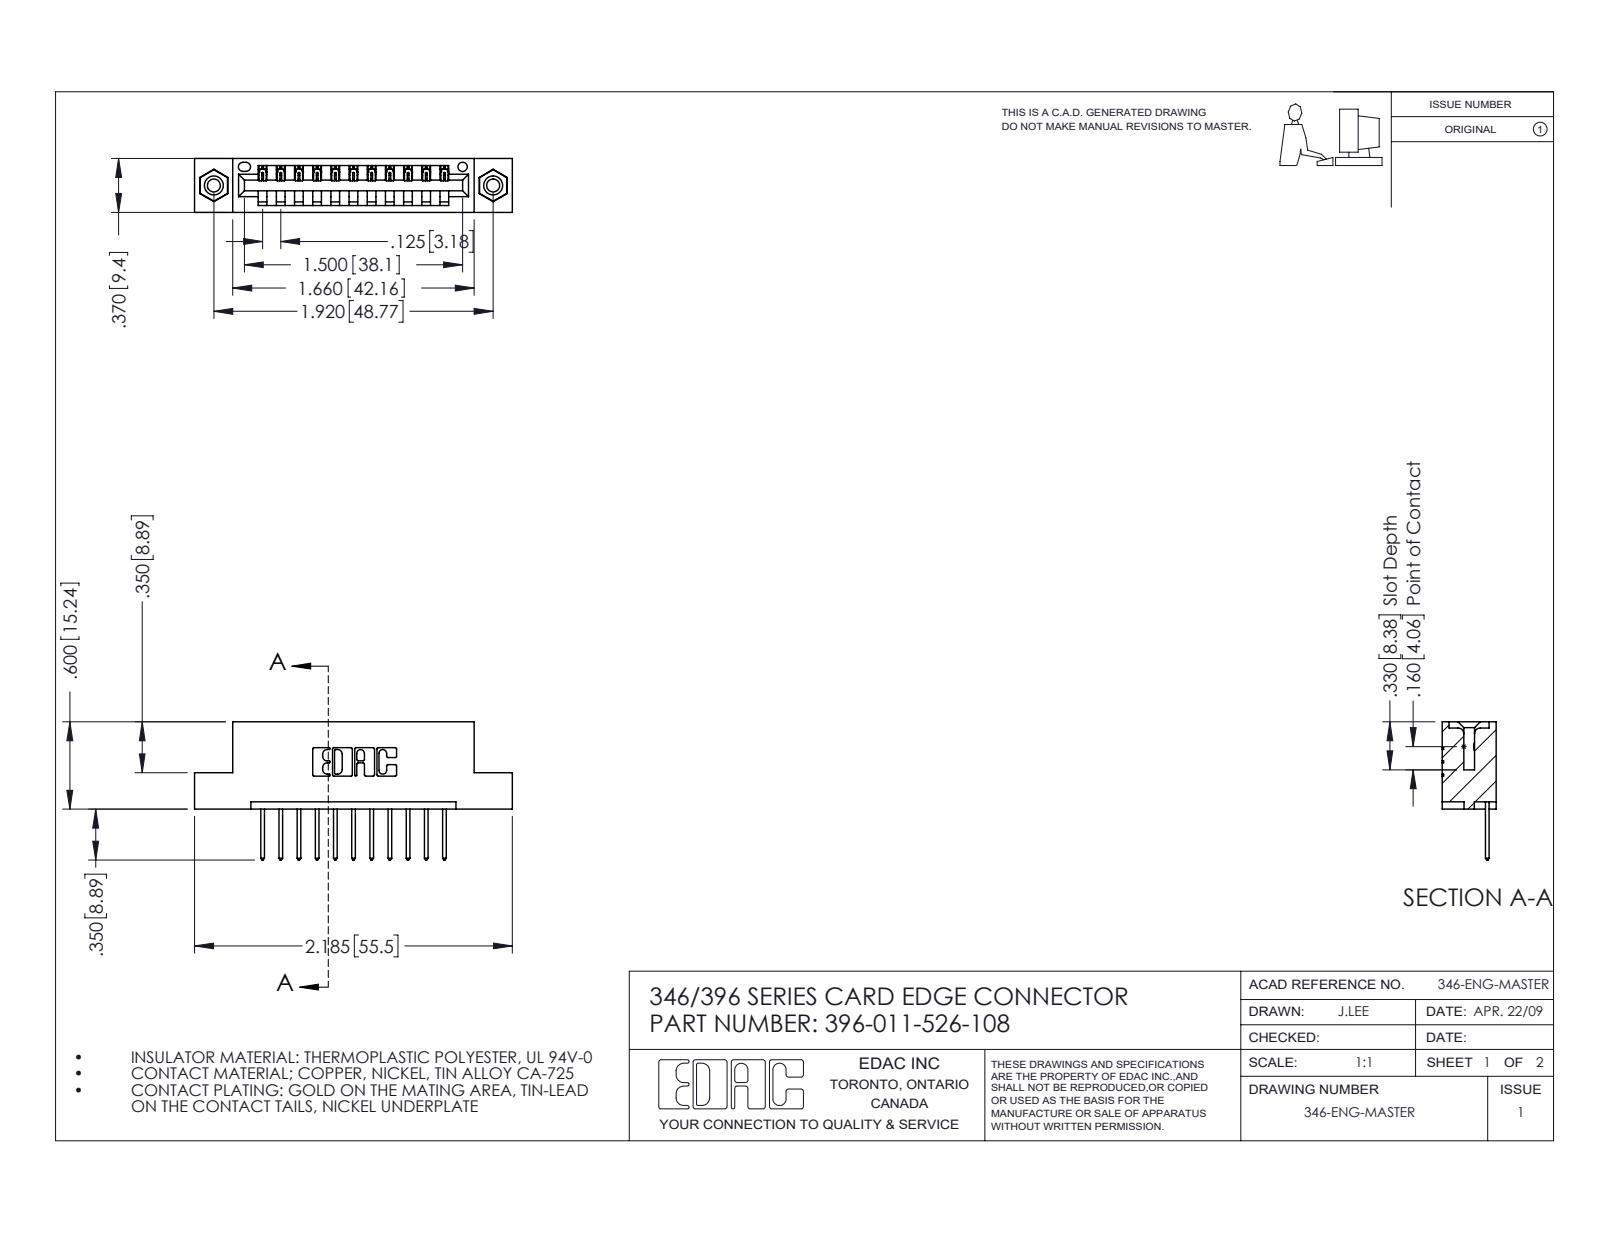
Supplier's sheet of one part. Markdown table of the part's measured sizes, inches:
| quantity | value |
| --- | --- |
| part name | 346 Part_Flush Mounting Lugs - 0.156 Dia-TI; 345-292-001_345-293-126; 396-011-526-108; 345-250-001_345-250-003-102 |
| STEP written by | SolidWorks 2016 (CONFIG_CONTROL_DESIGN) |
| units | inches |
| bodies | 14 solids, 820 faces (548 planar, 256 cylindrical, 16 other) |
| overall size | 2.185 × 0.95 × 0.37 |
| volume | 0.31 in³ |
| surface area | 9.347 in² |
| round holes (diameter × count) | 0.089 × 2, 0.125 × 2, 0.156 × 2, 0.064 × 1 |
| round bosses / shafts (diameter × count) | 0.155 × 2 |
| partial cylindrical surfaces (radius × count) | 0.006 × 22, 0.01 × 22, 0.01 × 22, 0.007 × 6, 0.031 × 6, 0.026 × 3, 0.031 × 2, 0.04 × 2 |
| main face-to-face distances | 0.25, 0.048, 0.322, 0.37, 0.072, 0.298, 0.025, 0.148, 0.222, 0.1 |
| hole center spacings | 0.246, 1.715, 1.92 |
